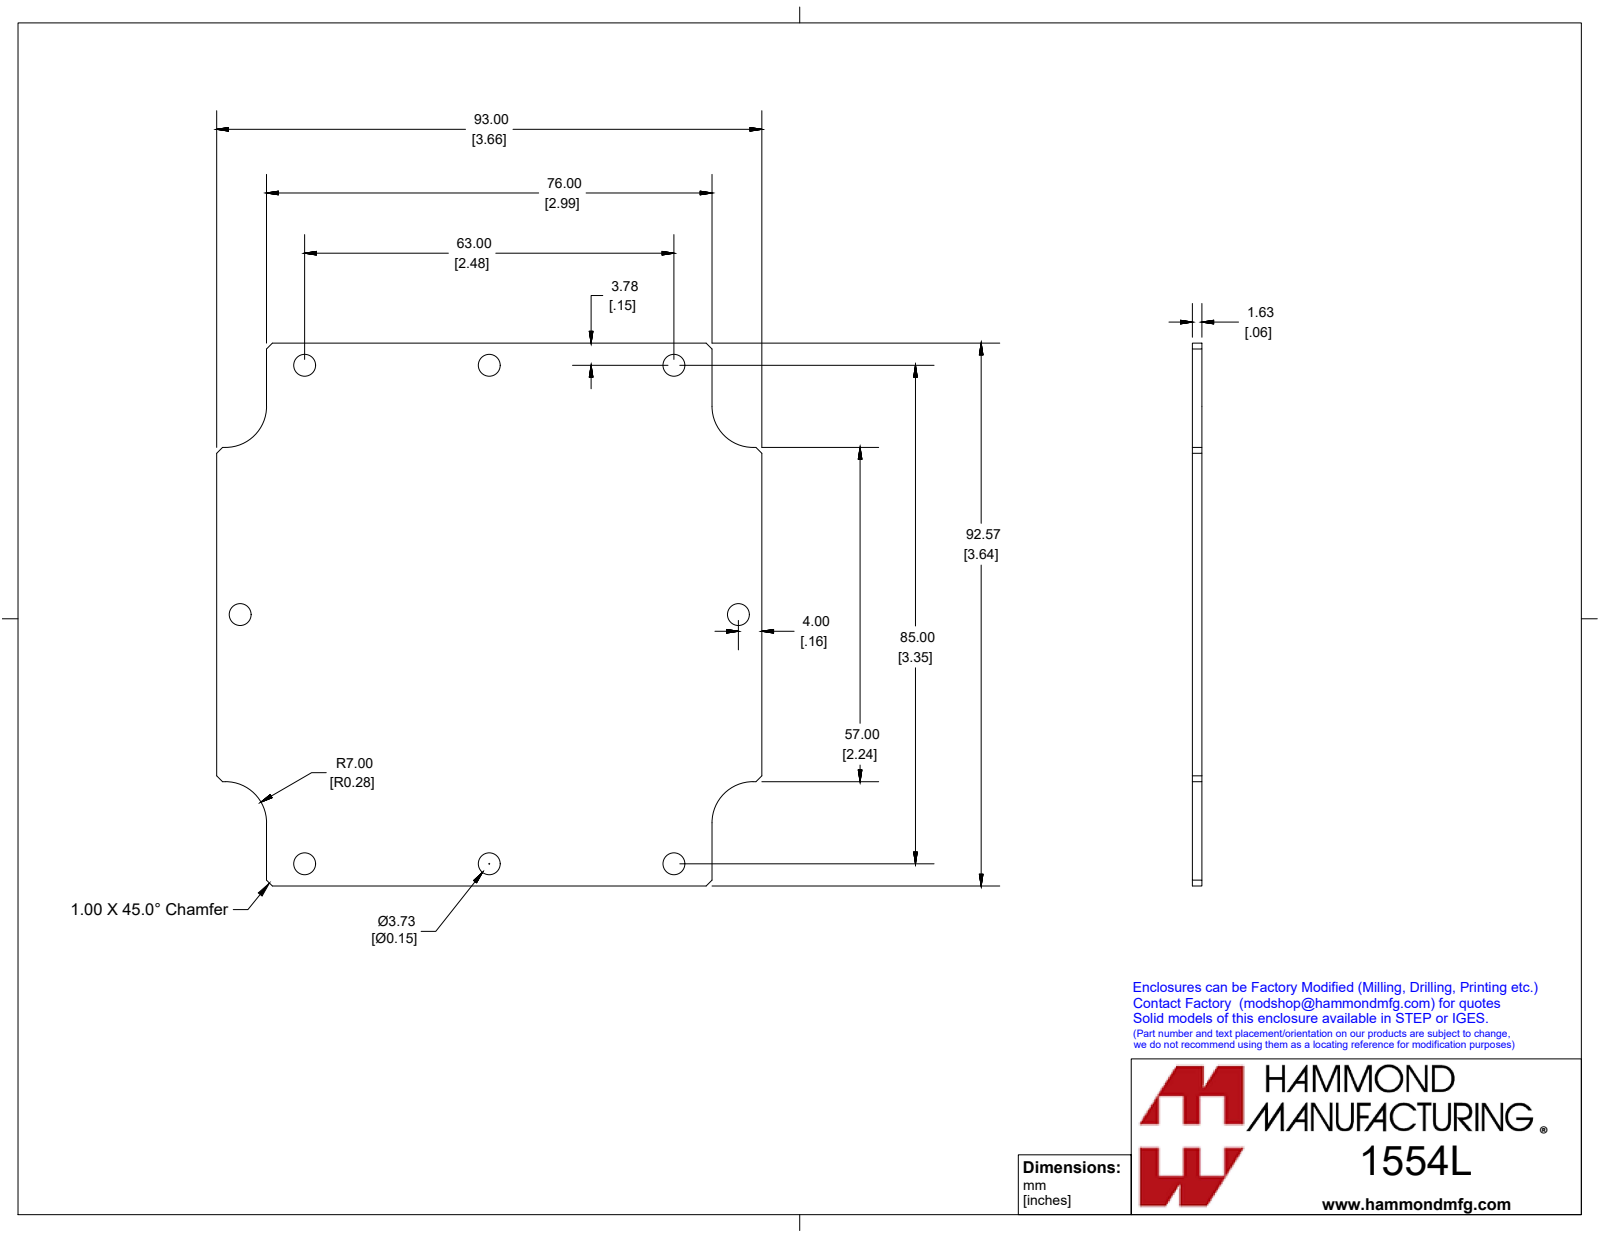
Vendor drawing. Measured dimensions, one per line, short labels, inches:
name: 1554LPL
written by: SolidWorks 2019 (CONFIG_CONTROL_DESIGN)
unit: in
bodies: 1 solid, 34 faces (22 planar, 12 cylindrical, 0 other)
size: 3.661 × 3.644 × 0.064
volume: 0.789 in³; area: 25.79 in²
holes: 8× ⌀0.147
rounds: 4× R0.276
face distances: 0.064, 3.644, 3.661, 0.335, 3.327, 2.992, 0.258, 4.378, 4.12, 4.636
hole spacings: 1.24, 1.728, 2.366, 3.346, 3.36, 3.569, 2.48, 4.165
